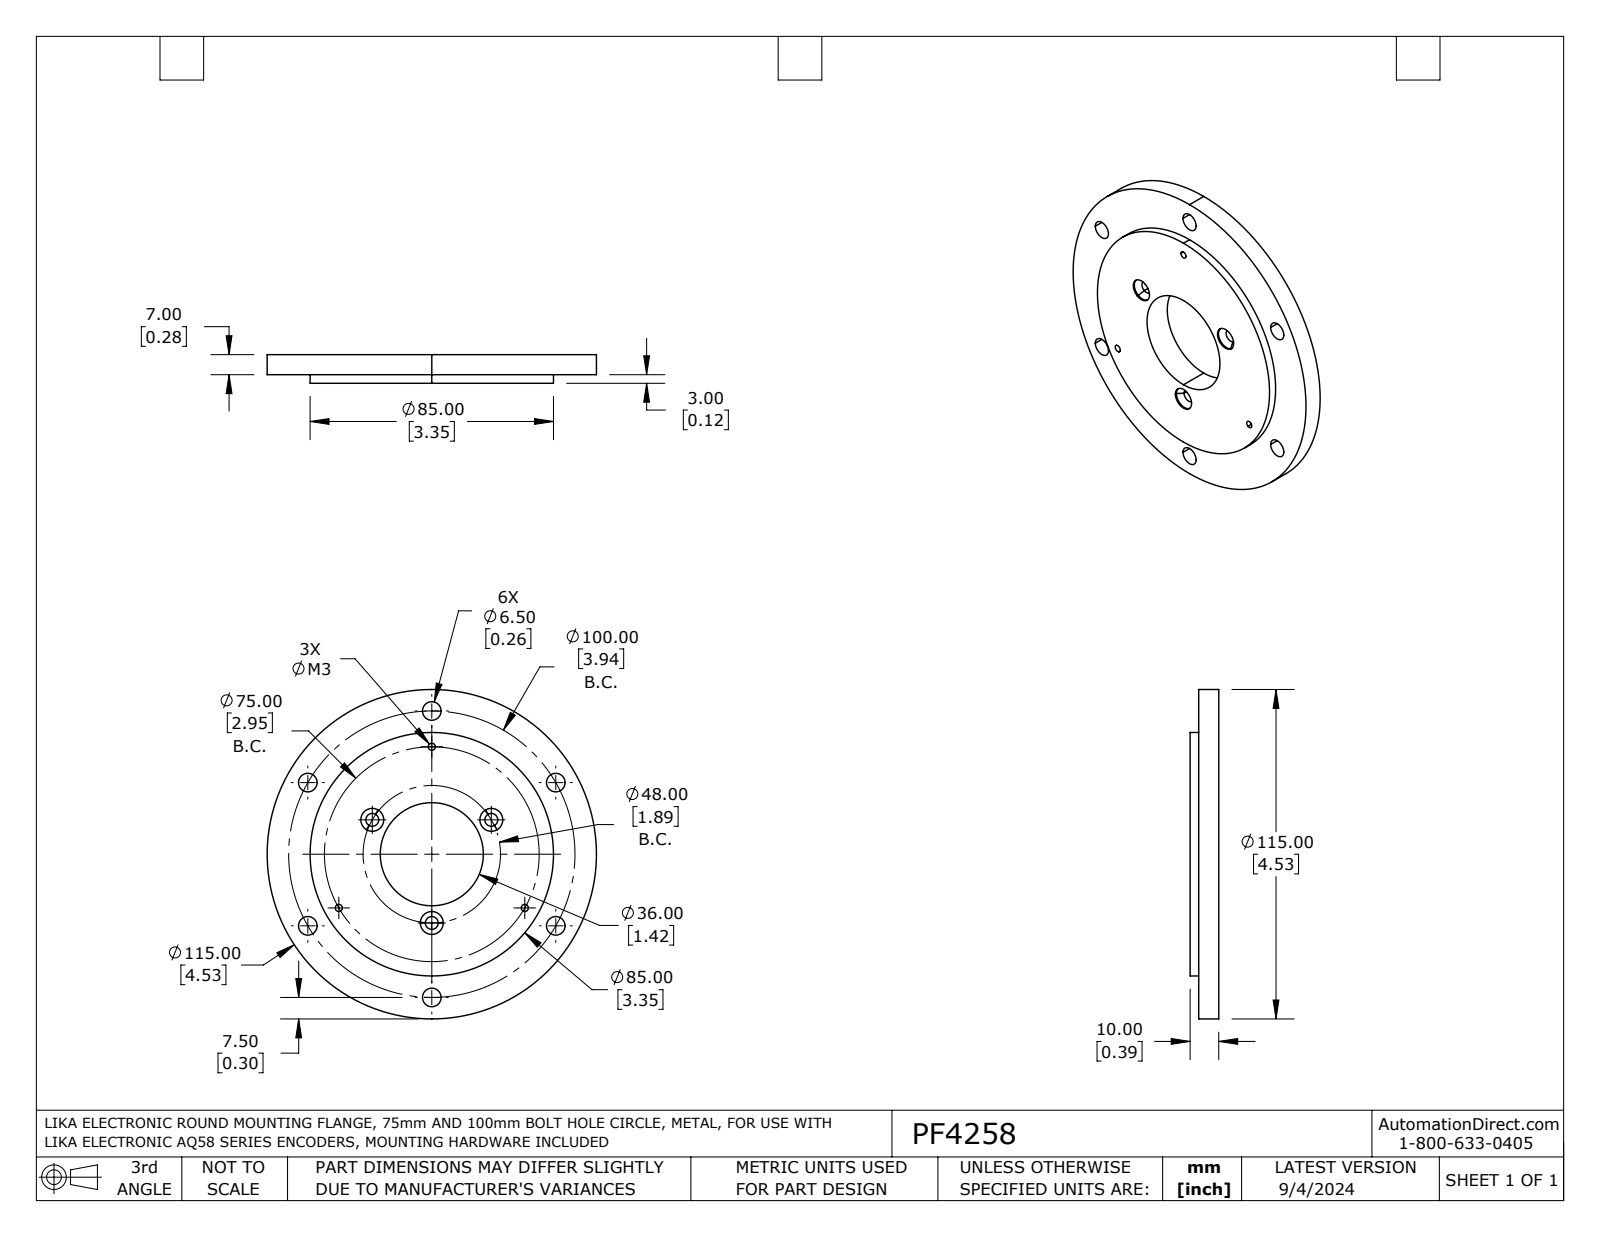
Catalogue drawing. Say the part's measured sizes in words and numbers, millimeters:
The part is named "PF4258". Its 3-D file was written by "SolidWorks 2021 (AUTOMOTIVE_DESIGN)". It is 1 solid with 56 faces: 3 planar, 45 cylindrical and 8 other. Overall it measures 115 by 115 by 10 millimeters. Its volume is 77 400 cubic millimeters and its surface area 24 180 square millimeters. Round holes: 6 of diameter 6.5, 3 of diameter 2.5, 3 of diameter 4.5, 3 of diameter 8, 1 of diameter 36. Round bosses or shafts: 1 of diameter 115, 1 of diameter 85. The main face-to-face distances are 7, 10, 3. The hole center spacings are 50, 43.3, 45.1, 65.4, 86.6, 32.9, 76, 12.5.
